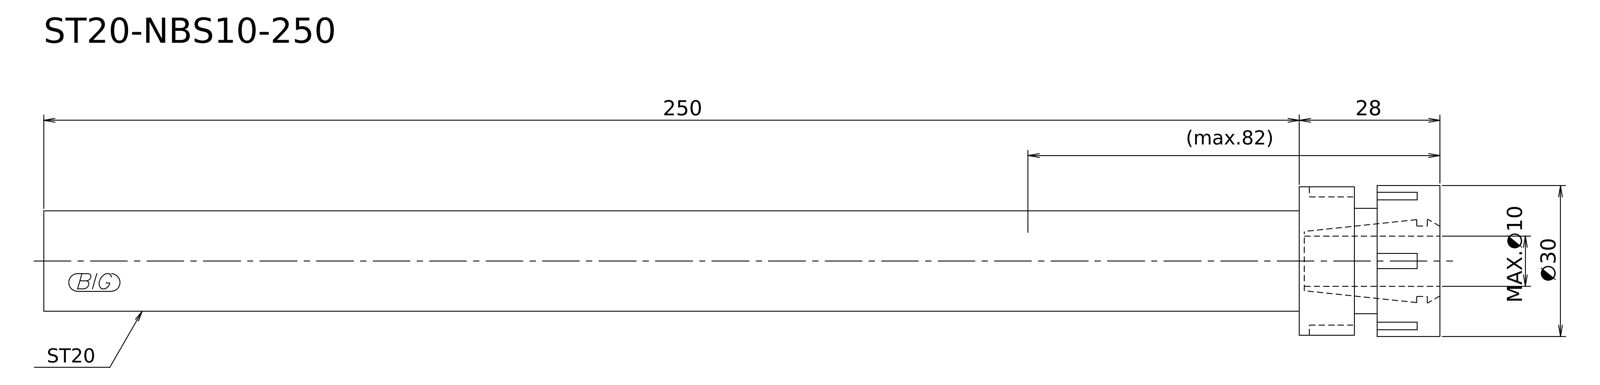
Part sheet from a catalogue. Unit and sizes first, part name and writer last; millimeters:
Units: millimetres
Overall size (bounding box): 278 × 30 × 30
Round bosses / shafts (diameter × count): ⌀30 ×1, ⌀29.5 ×1, ⌀21 ×1, ⌀20 ×1
Main face-to-face distances: 28, 12.5, 15.5, 17, 4.5, 11, 278, 265.5, 261, 250
Volume: 96 453 mm³ · Surface area: 20 290 mm²
Bodies: 1 solid, 9 faces (5 planar, 4 cylindrical, 0 other)
STEP written by: Kubotek KeyCreator V8.5.1 (14335) (CONFIG_CONTROL_DESIGN)
